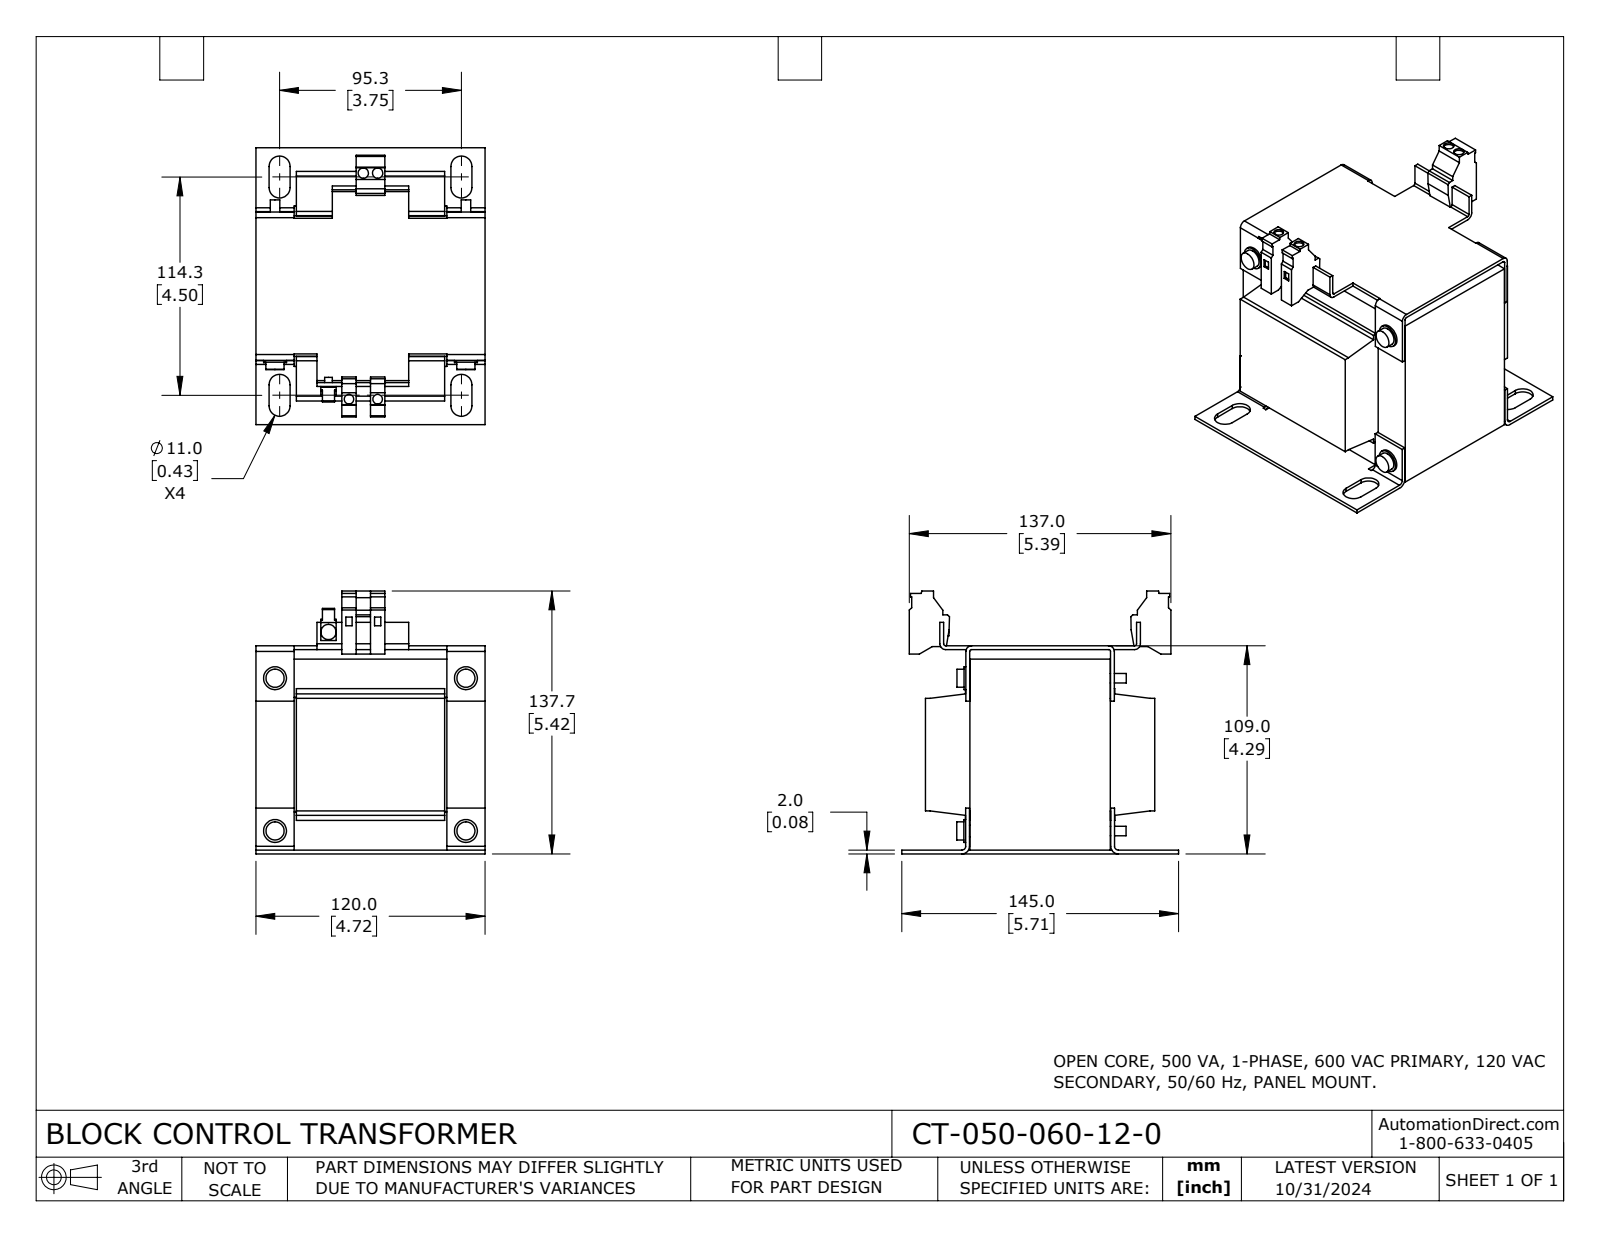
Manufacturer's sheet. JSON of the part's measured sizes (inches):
{"part_name": "CT-050-060-12-0", "step_written_by": "SolidWorks 2023 (CONFIG_CONTROL_DESIGN)", "units": "inches", "bodies": {"solids": 1, "faces": 322, "planar": 237, "cylindrical": 85, "other": 0}, "overall_size": [5.709, 5.421, 4.724], "volume_in3": 71.25, "surface_area_in2": 241.4, "round_holes": [[0.197, 2], [0.213, 2]], "round_bosses_or_shafts": [[0.472, 4], [0.374, 4], [0.236, 4], [0.197, 4], [0.315, 1], [0.157, 1]], "partial_cylinders_radius": [[0.217, 8], [0.039, 4], [0.118, 4], [0.079, 2], [0.157, 2]], "face_to_face_distances": [0.079, 4.213, 3.937, 0.787, 0.833, 3.892, 3.15, 4.134, 4.291, 0.197], "hole_center_spacings": [4.671, 0.295, 0.591, 4.661, 4.699]}
